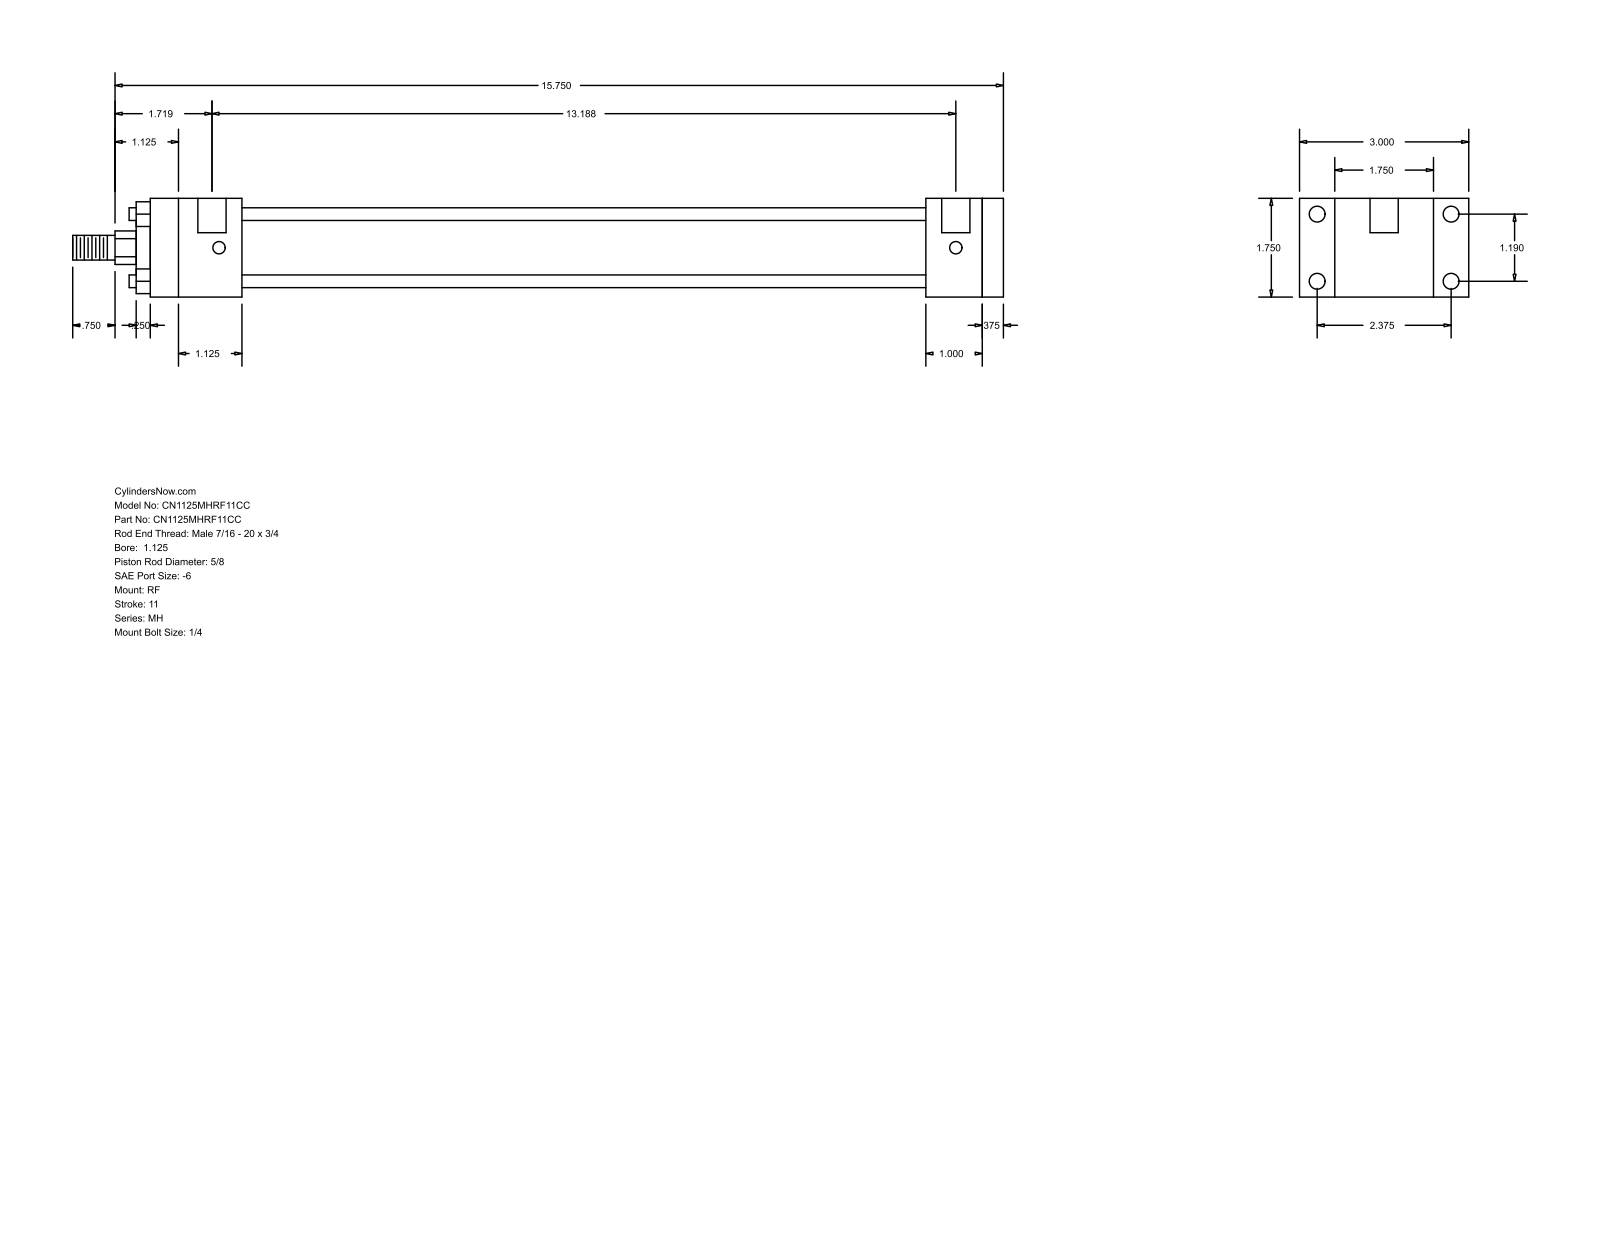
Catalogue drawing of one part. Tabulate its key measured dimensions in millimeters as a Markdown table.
| quantity | value |
| --- | --- |
| part name | MH_RF__0112_0.625 |
| STEP written by | GSSL Pune (CONFIG_CONTROL_DESIGN) |
| units | millimeters |
| bodies | 0 solids, 92 faces (64 planar, 28 cylindrical, 0 other) |
| overall size | 419.1 × 76.2 × 44.45 |
| round holes (diameter × count) | 5.56 × 4, 7.14 × 4, 12.7 × 2 |
| round bosses / shafts (diameter × count) | 5.71 × 4, 34.92 × 1, 28.57 × 1, 15.88 × 1, 11.11 × 1 |
| partial cylindrical surfaces (radius × count) | 7.54 × 1 |
| main face-to-face distances | 44.46, 9.53, 384.17, 25.4, 34.93, 15.87, 333.37, 342.9, 307.97, 41.27 |
| hole center spacings | 30.22, 60.32, 67.47, 331.79, 3.17, 334.96 |
